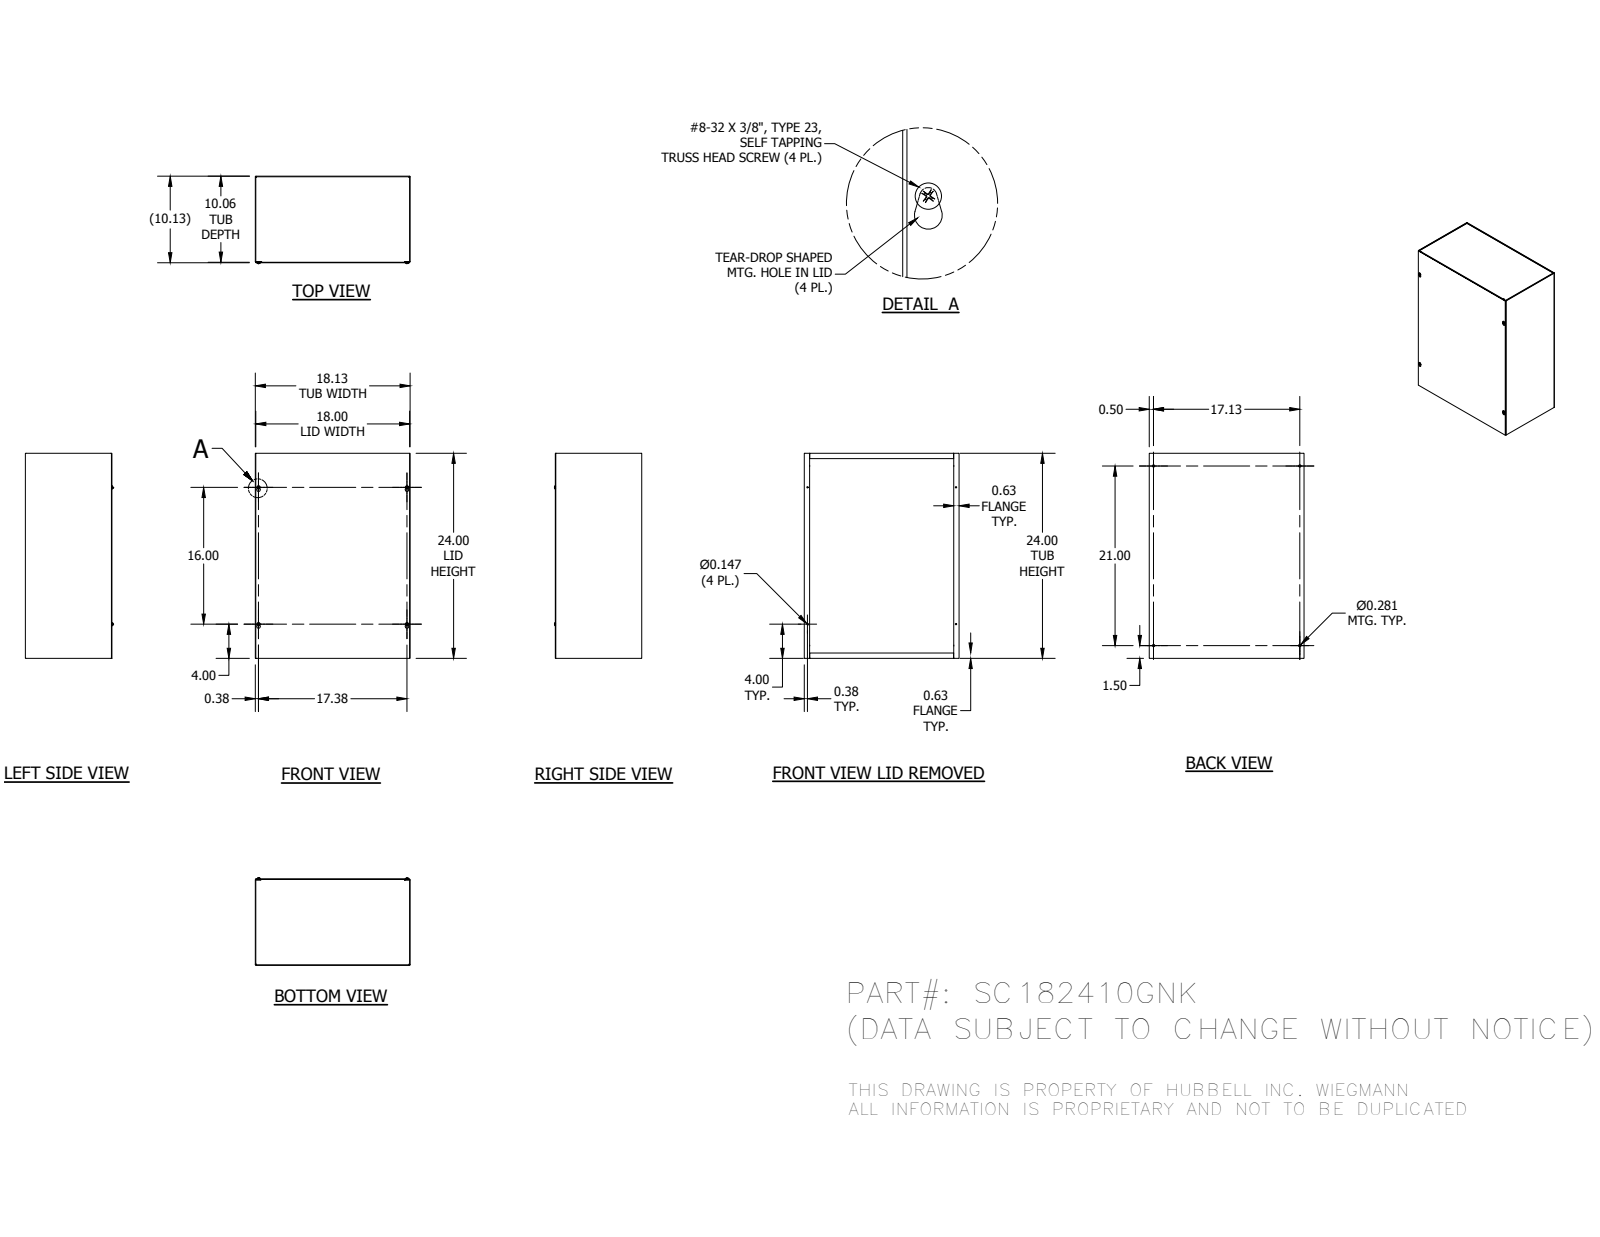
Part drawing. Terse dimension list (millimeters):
name: SC182410GNKBLR; SC1810GNKTB; SC1824GLPA; 34056 (+1 more)
written by: Autodesk Inventor 2014 (AUTOMOTIVE_DESIGN)
unit: mm
bodies: 8 solids, 268 faces (152 planar, 48 cylindrical, 68 other)
size: 609.6 × 460.38 × 259.72
volume: 1 834 000 mm³; area: 2 325 000 mm²
holes: 4× ⌀3.73, 4× ⌀7.14
bosses: 4× ⌀9.75, 4× ⌀4.17
rounds: 12× R0.4, 12× R1.98, 4× R3.17, 4× R5.16
face distances: 1.59, 254, 458.79, 1.58, 255.59, 255.58, 257.17, 608.01, 457.2, 460.38
hole spacings: 63.58, 442.73, 469.91, 642.48, 406.4, 434.98, 441.32, 533.4
